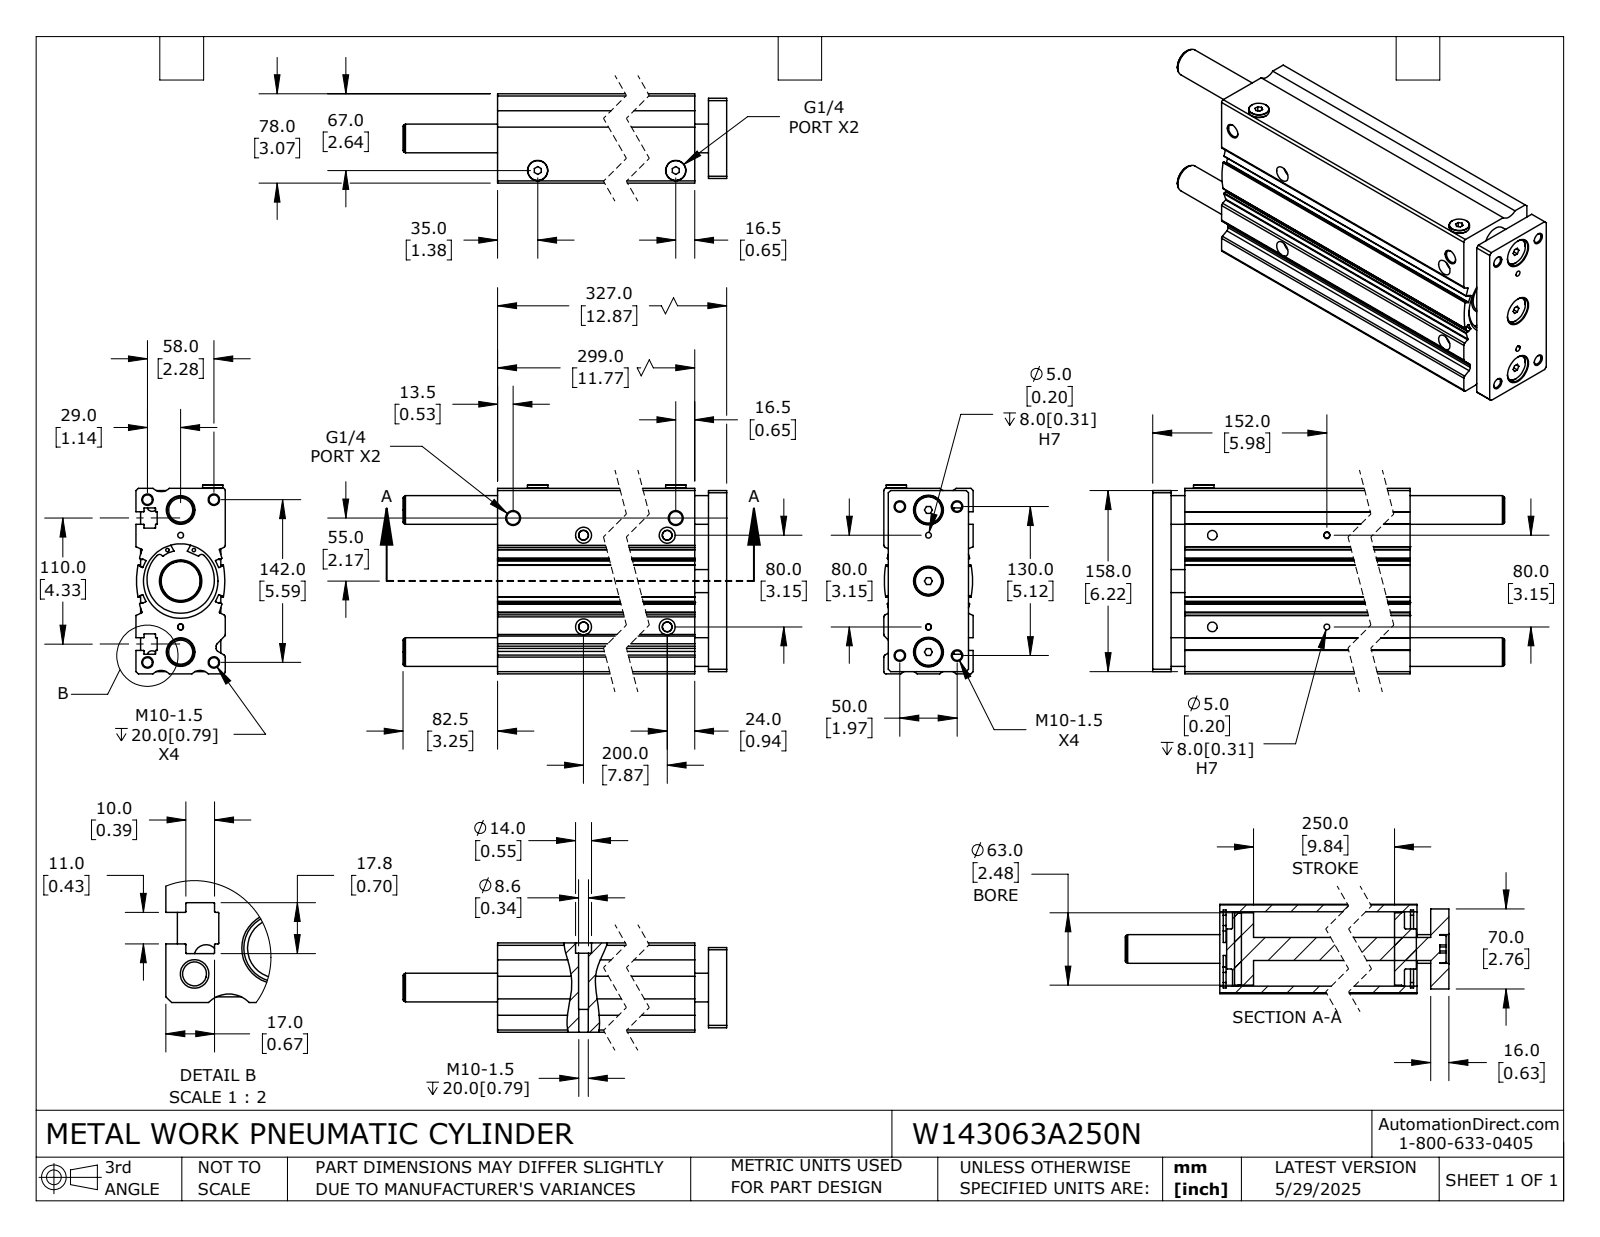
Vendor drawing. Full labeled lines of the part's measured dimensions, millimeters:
Part name (STEP PRODUCT): W143063A250N_ROD; W143063A250N; W143063A250N_BODY
STEP written by: SolidWorks 2024 (CONFIG_CONTROL_DESIGN)
Units: millimetres
Bodies: 6 solids, 454 faces (182 planar, 216 cylindrical, 56 other)
Overall size (bounding box): 409.5 × 165 × 78
Volume: 2 896 000 mm³ · Surface area: 476 100 mm²
Round holes (diameter × count): ⌀8.4 ×12, ⌀3 ×4, ⌀5 ×4, ⌀8.6 ×4, ⌀14 ×4, ⌀25 ×3, ⌀11.4 ×2, ⌀65 ×1
Round bosses / shafts (diameter × count): ⌀24 ×3, ⌀17.7 ×2, ⌀68 ×1, ⌀64.8 ×1, ⌀63 ×1, ⌀35 ×1, ⌀20 ×1
Partial cylindrical surfaces — rounded edges, fillets, slot ends (radius × count): R0.3 ×44, R0.5 ×12, R2 ×8, R2.5 ×4, R3 ×4, R10 ×3, R3.1 ×2, R29.4 ×2
Main face-to-face distances: 78, 162, 110, 16, 3.4, 14.4, 18.5, 12, 28, 327
Hole centre spacings: 7.2, 17.3, 25.2, 29.4, 30.4, 35.4, 36.8, 40.3
